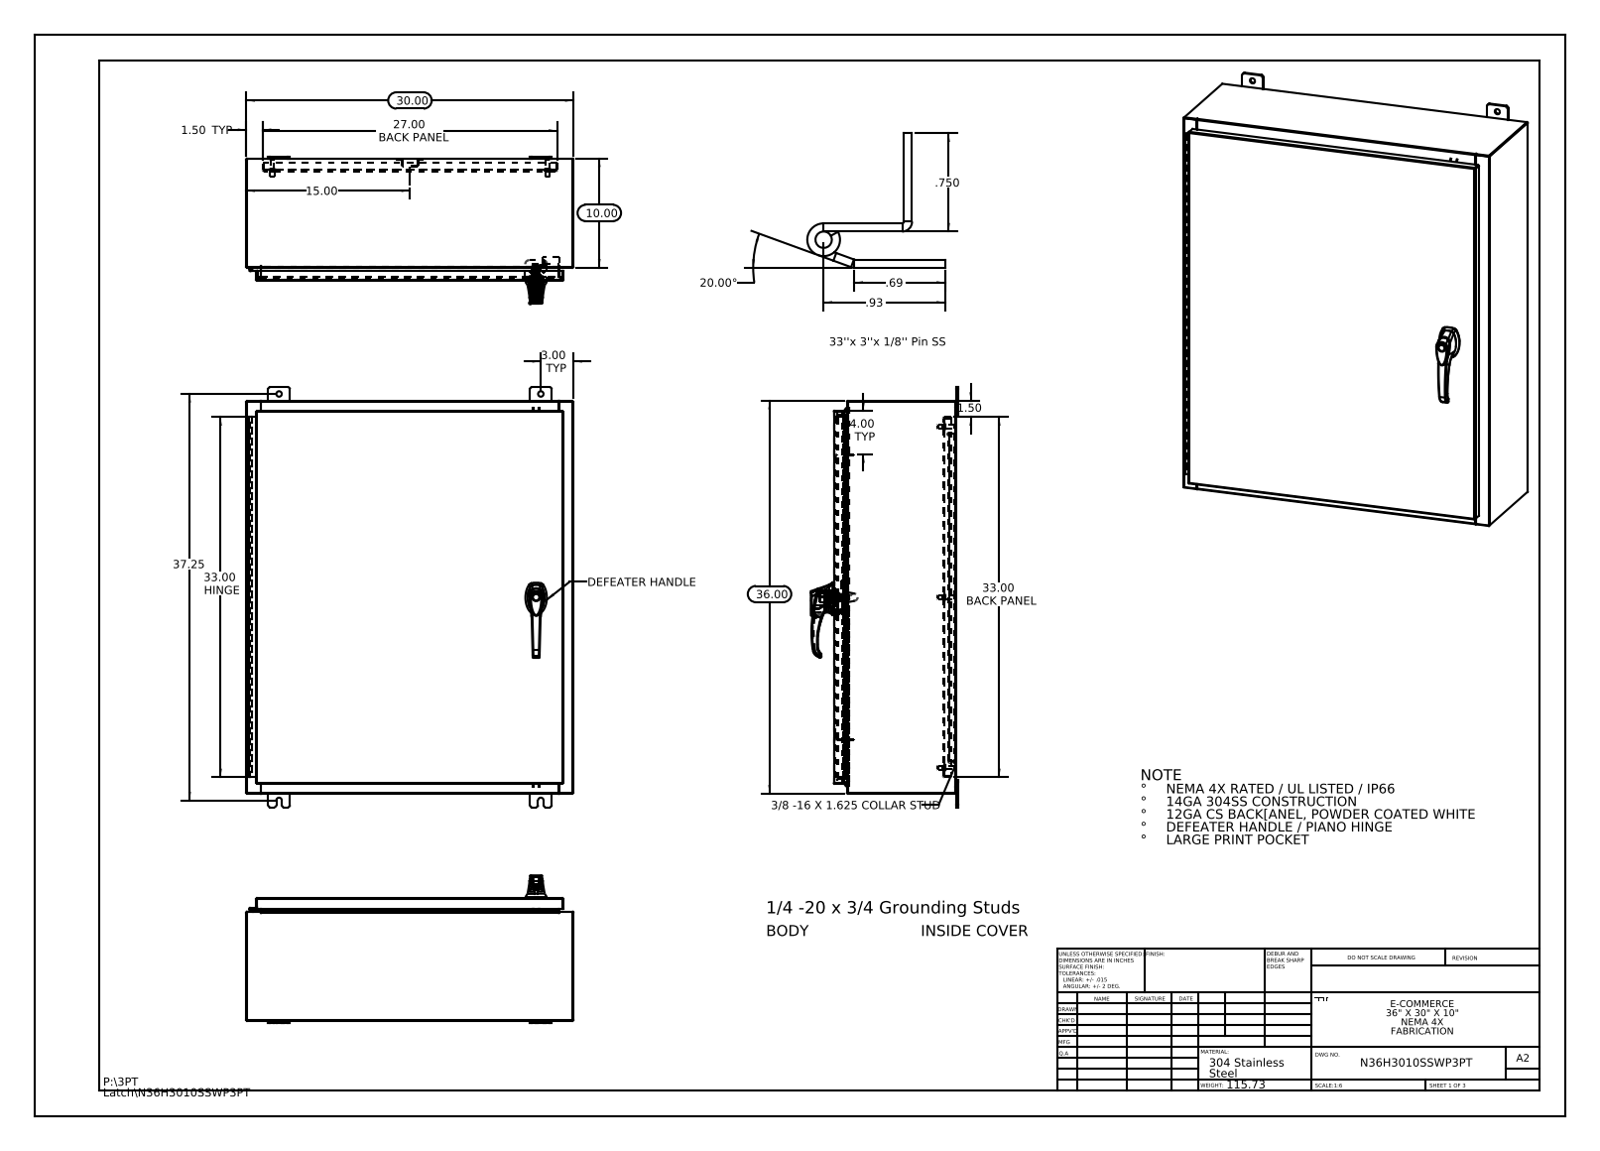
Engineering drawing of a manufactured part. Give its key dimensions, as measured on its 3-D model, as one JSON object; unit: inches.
{"part_name": "N36H3010SSWP3PT Defeater Handle - 3 - 2500-51 ZN; 26161102; N36H3010SSWP3PT 263033_Industrilas; N36H3010SSWP3PT Enclosure Stiffener (+8 more)", "step_written_by": "SolidWorks 2013 (CONFIG_CONTROL_DESIGN)", "units": "inches", "bodies": {"solids": 34, "faces": 2808, "planar": 1065, "cylindrical": 1069, "other": 674}, "overall_size": [38.5, 30, 13.495], "volume_in3": 408.9, "surface_area_in2": 10129, "round_holes": [[0.5, 10], [0.25, 4], [0.138, 3], [0.161, 3], [0.079, 2], [0.203, 2], [0.313, 2], [0.437, 2], [0.125, 1], [0.125, 1], [0.197, 1], [0.276, 1]], "round_bosses_or_shafts": [[0.625, 6], [0.375, 6], [0.33, 6], [1.181, 1], [0.748, 1], [0.68, 1], [0.661, 1], [0.639, 1]], "partial_cylinders_radius": [[0.118, 37], [0.006, 33], [0.013, 28], [0.19, 24], [0.088, 22], [0.039, 15], [0.028, 12], [0.008, 6]], "face_to_face_distances": [0.075, 11.126, 11.051, 0.104, 11.201, 1, 10.126, 1.075, 10.051, 1.179], "hole_center_spacings": [11.363, 13.669, 15.625, 29.694, 25.25, 28.129, 0.295, 0.625]}
